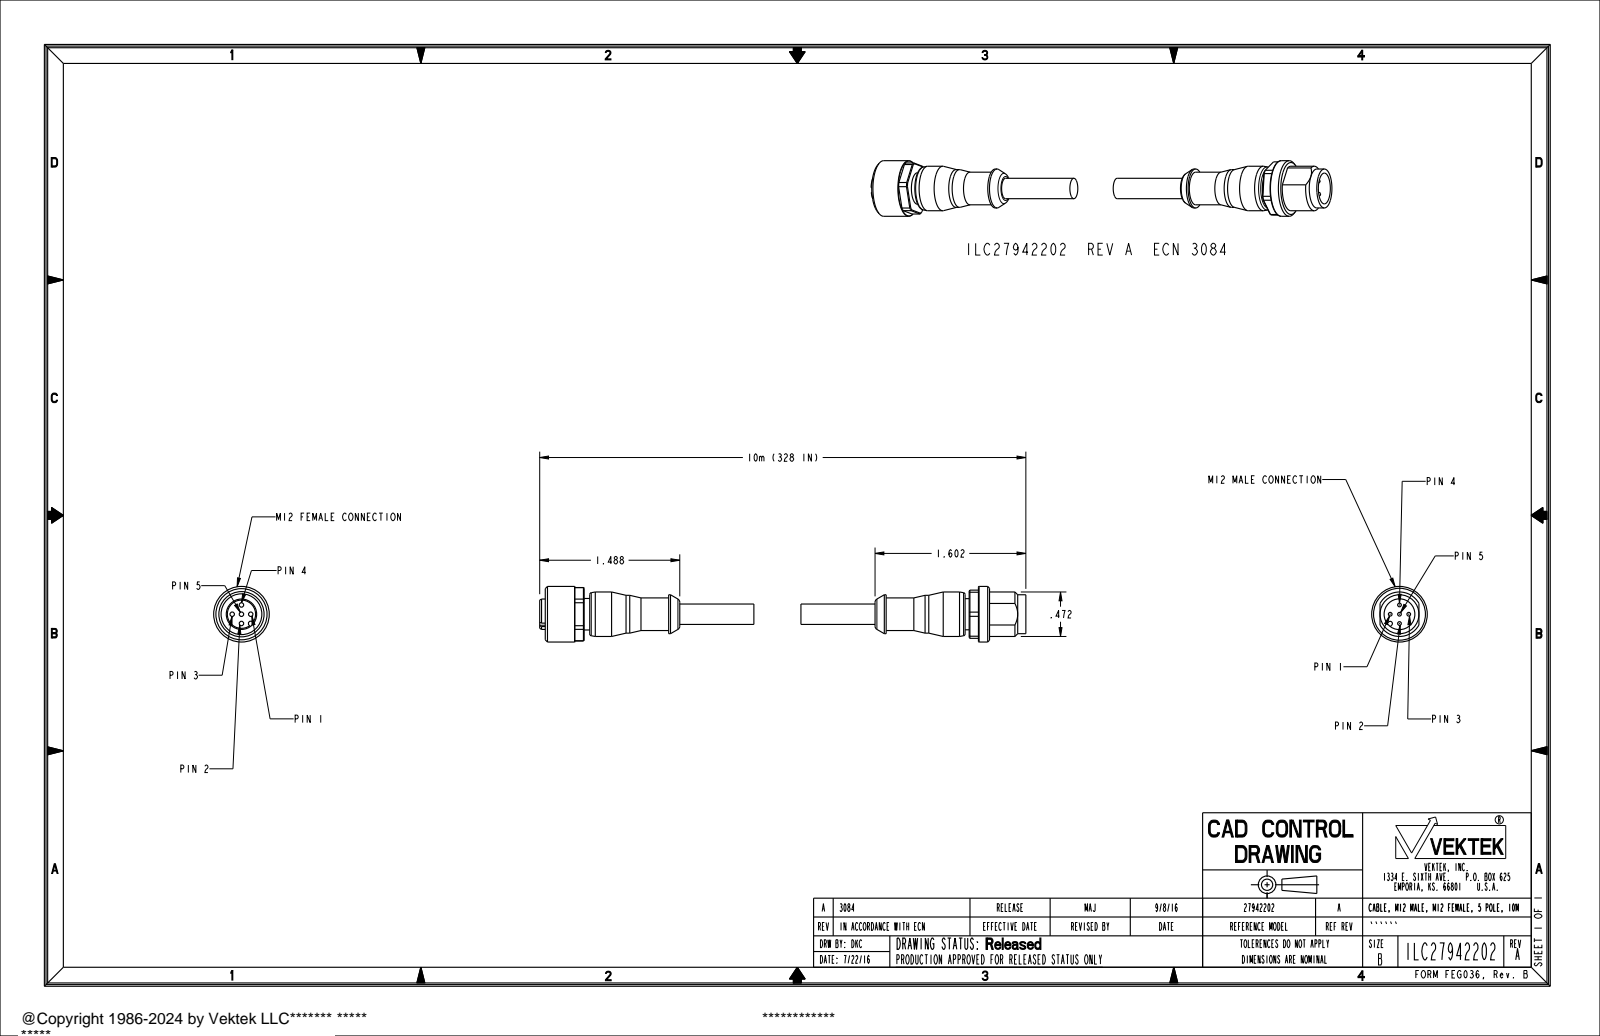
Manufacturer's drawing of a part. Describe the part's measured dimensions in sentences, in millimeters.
The part is named "27942202_1; 27942202_2; ILC27942202". Its 3-D file was written by "PRO/ENGINEER BY PARAMETRIC TECHNOLOGY CORPORATION, 2013320 (AUTOMOTIVE_DESIGN)". It is 2 solids with 203 faces: 60 planar, 72 cylindrical and 71 other. Overall it measures 131.2 by 15 by 15 millimeters. Its volume is 8 000 cubic millimeters and its surface area 5 164 square millimeters. Round holes: 5 of diameter 1.2, 1 of diameter 8.3, 1 of diameter 11. Round bosses or shafts: 5 of diameter 1, 1 of diameter 15, 1 of diameter 12, 1 of diameter 10.5, 1 of diameter 10.2, 1 of diameter 8.8, 1 of diameter 8.5, 1 of diameter 8.4. Partial cylindrical surfaces (rounded edges, fillets, slot ends): 1 of radius 0.6, 1 of radius 0.7, 1 of radius 7.2. The main face-to-face distances are 13, 3, 103.9, 10.5, 113.3, 12, 109.4, 7.5, 1.5, 2.5. The hole center spacings are 2.5, 3.5, 5.
